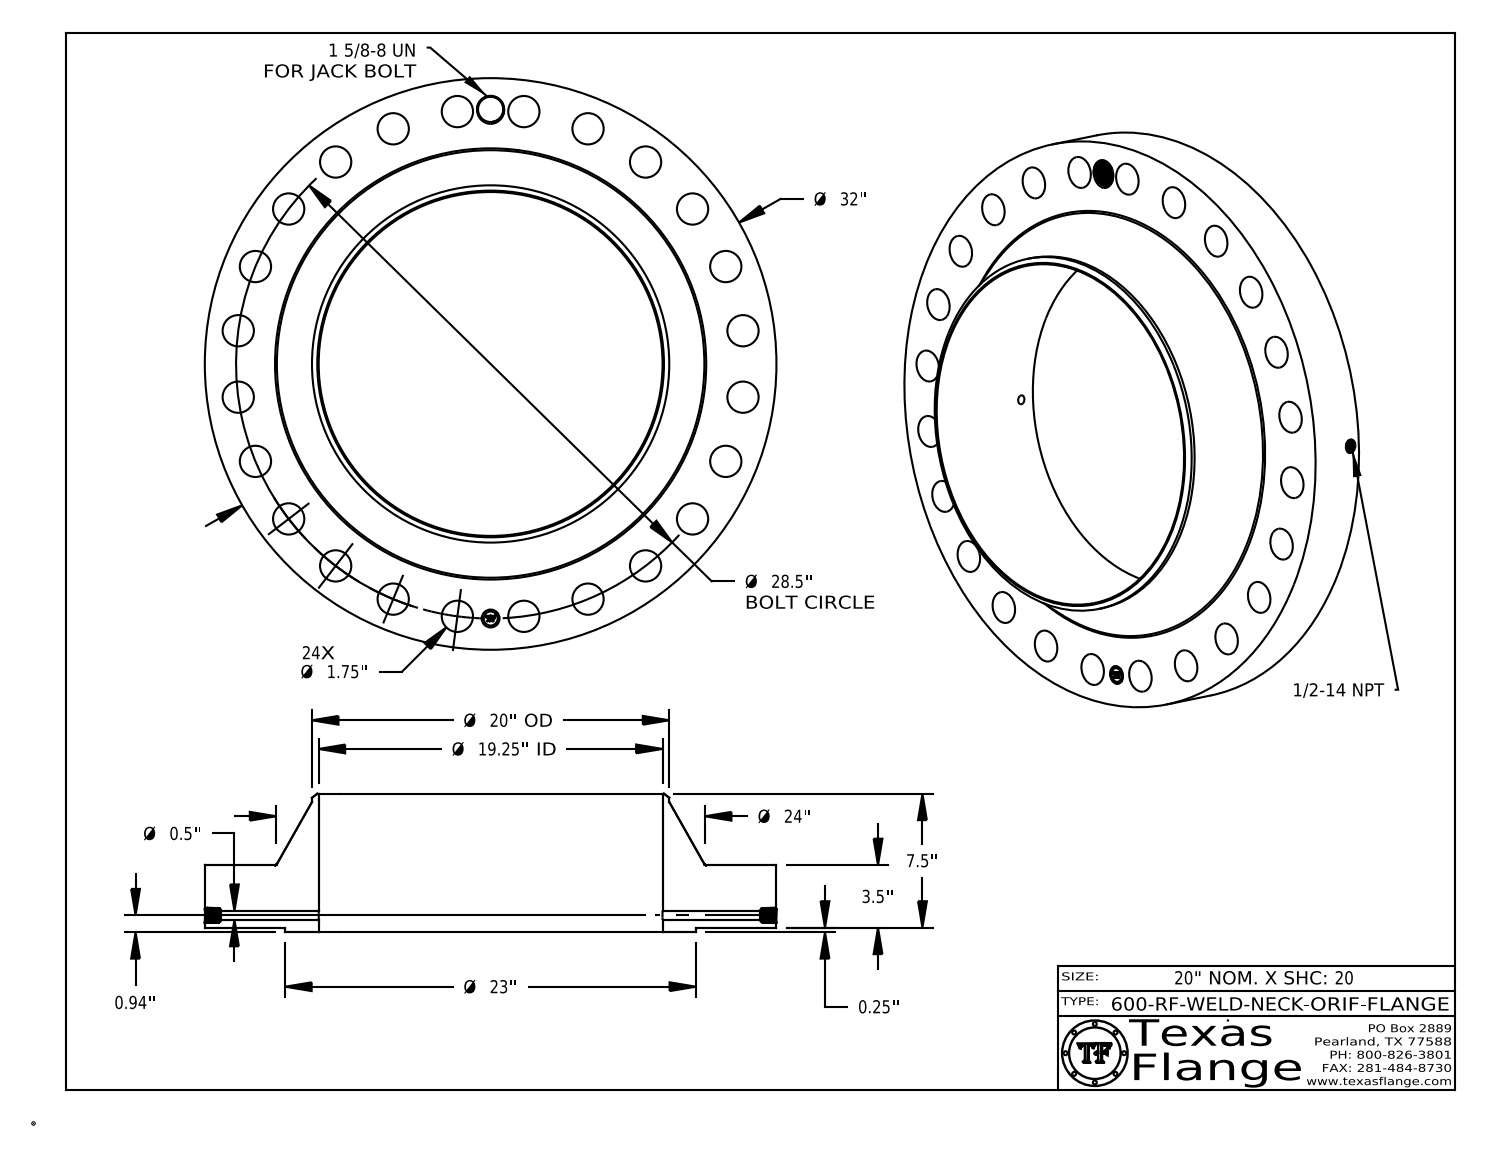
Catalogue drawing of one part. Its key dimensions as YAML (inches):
part_name: "600-RF-WELD-NECK"
step_written_by: "CATIA V5 STEP AP214 (AUTOMOTIVE_DESIGN)"
units: inches
bodies: {solids: 1, faces: 879, planar: 369, cylindrical: 151, other: 359}
overall_size: [32, 32, 7.75]
volume: 1944
surface_area: 2426
round_holes:
  - {diameter: 1.75, count: 24}
  - {diameter: 0.5, count: 1}
  - {diameter: 0.672, count: 1}
  - {diameter: 1, count: 1}
  - {diameter: 1.409, count: 1}
  - {diameter: 19.25, count: 1}
round_bosses_or_shafts:
  - {diameter: 0.061, count: 8}
  - {diameter: 32, count: 1}
  - {diameter: 23, count: 1}
  - {diameter: 20, count: 1}
  - {diameter: 0.788, count: 1}
face_to_face_distances: [3.5, 0.25, 3.75, 7.75, 7.5, 4, 3.735, 3.485, 0.015, 4.015]
hole_center_spacings: [14.25, 17.35, 24.681, 28.256, 10.906, 3.72, 7.376, 20.152]
